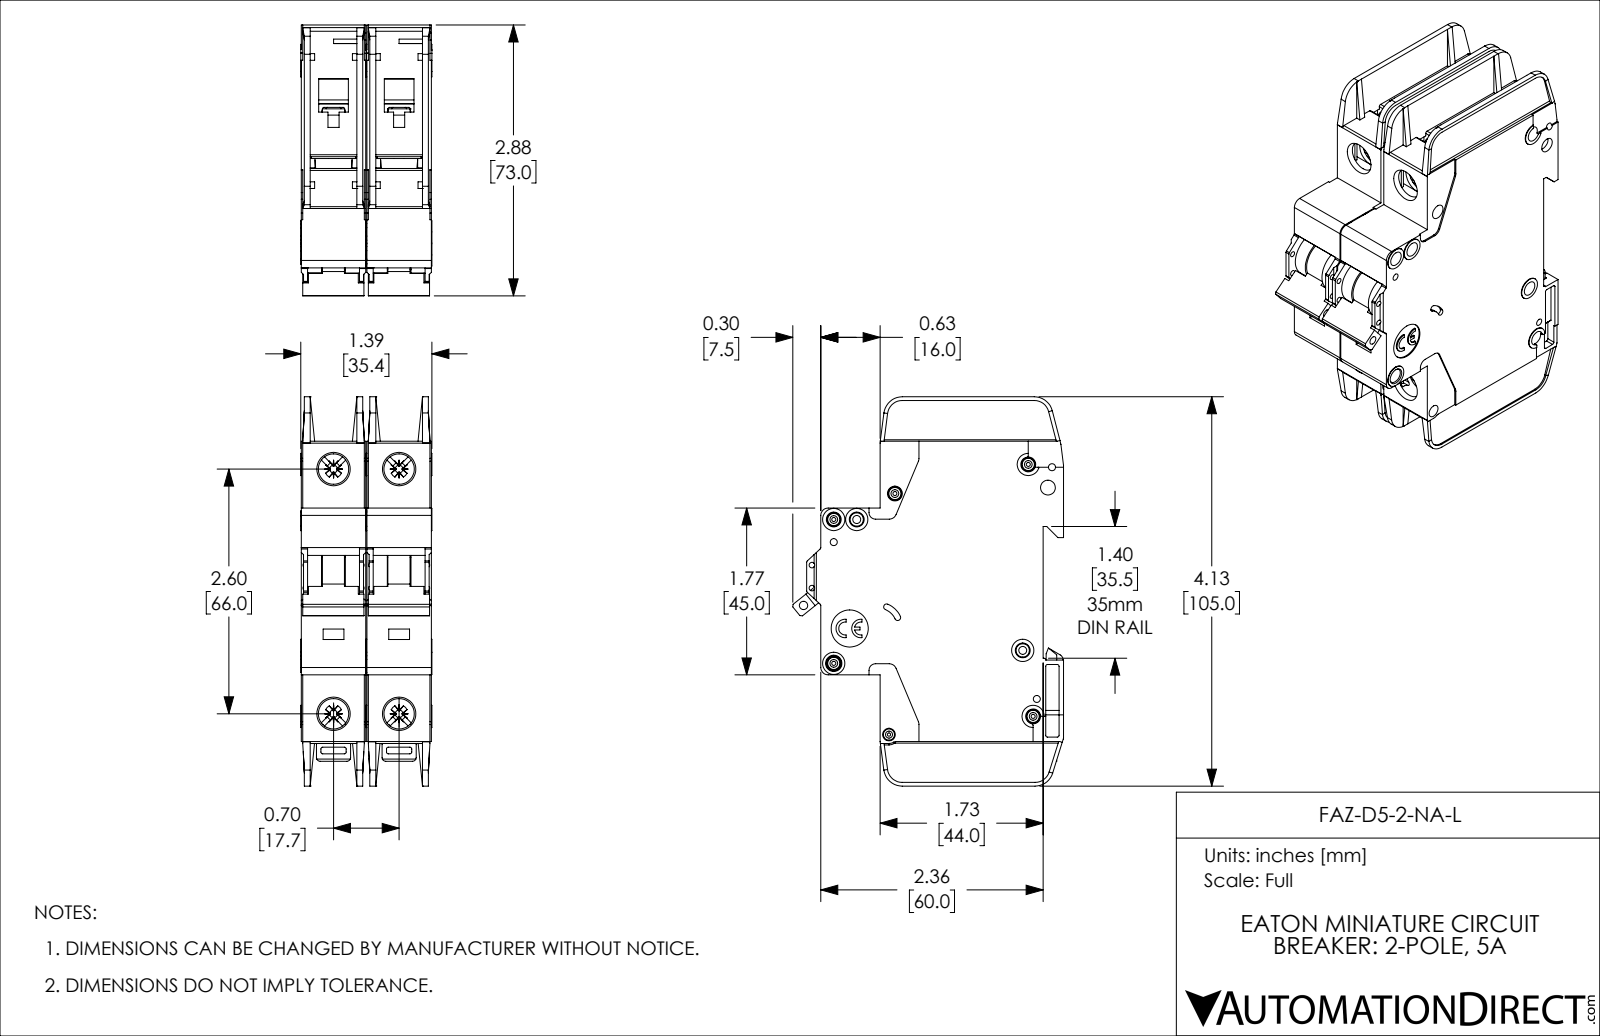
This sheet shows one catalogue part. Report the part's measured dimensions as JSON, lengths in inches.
{"part_name": "FAZ-D5-2-NA-L", "step_written_by": "SolidWorks 2019 (AUTOMOTIVE_DESIGN)", "units": "inches", "bodies": {"solids": 2, "faces": 2254, "planar": 1342, "cylindrical": 714, "other": 198}, "overall_size": [4.134, 2.876, 1.394], "volume_in3": 9.365, "surface_area_in2": 82.01, "round_holes": [[0.157, 8], [0.043, 5], [0.075, 4], [0.323, 4], [0.059, 2], [0.085, 2], [0.035, 1], [0.089, 1], [0.098, 1], [0.134, 1], [0.394, 1]], "round_bosses_or_shafts": [[0.13, 5], [0.236, 4], [0.118, 3], [0.098, 2]], "partial_cylinders_radius": [[0.02, 57], [0.016, 20], [0.039, 14], [0.079, 10], [0.043, 8], [0.008, 5], [0.197, 5], [0.01, 4]], "face_to_face_distances": [0.697, 0.047, 0.685, 0.591, 0.094, 0.638, 0.543, 1.382, 0.744, 0.65], "hole_center_spacings": [0.244, 0.537, 0.697, 0.87, 2.598, 2.69, 0.189, 0.199]}
